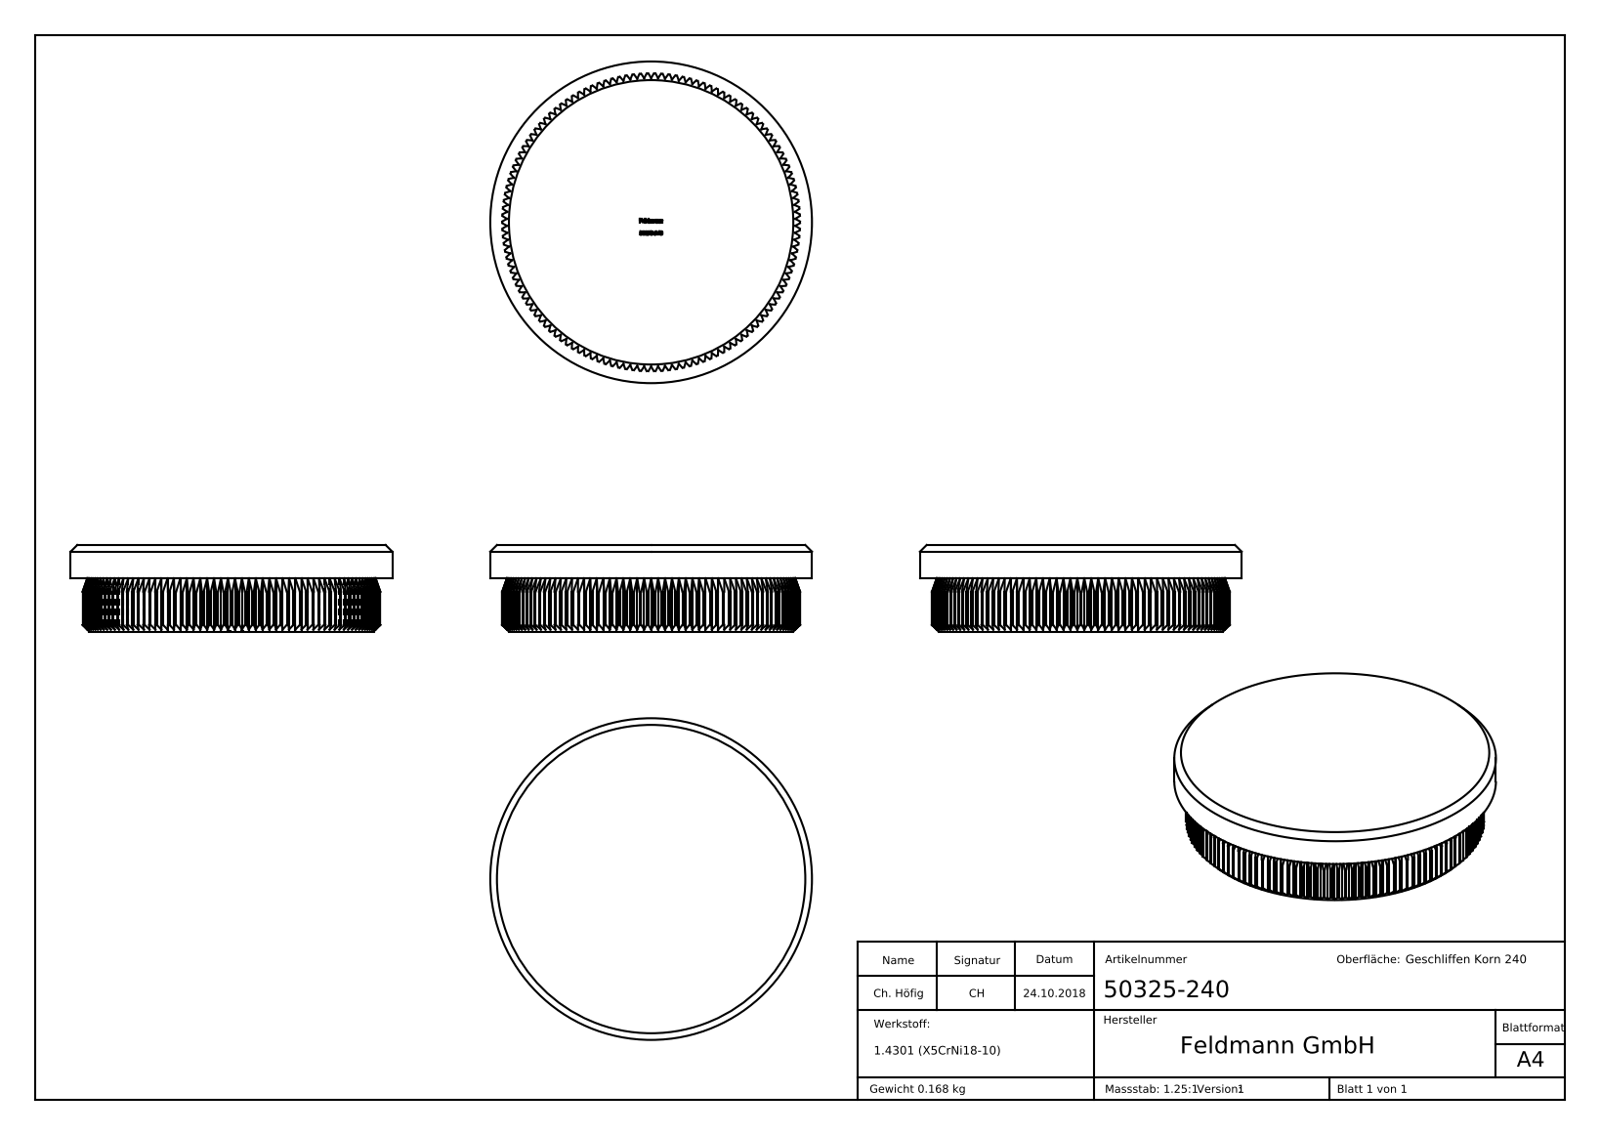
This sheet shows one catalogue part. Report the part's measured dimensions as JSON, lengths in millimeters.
{"part_name": "50325-240", "step_written_by": "SolidWorks 2015 (CONFIG_CONTROL_DESIGN)", "units": "millimeters", "bodies": {"solids": 1, "faces": 782, "planar": 401, "cylindrical": 132, "other": 249}, "overall_size": [48.3, 48.3, 13], "volume_mm3": 21258, "surface_area_mm2": 6129, "round_bosses_or_shafts": [[48.3, 1]], "partial_cylinders_radius": [[22.35, 1]], "face_to_face_distances": [13, 8, 5, 21.66, 21.64, 21.68, 21.62, 7.9, 12.9, 1.64]}
